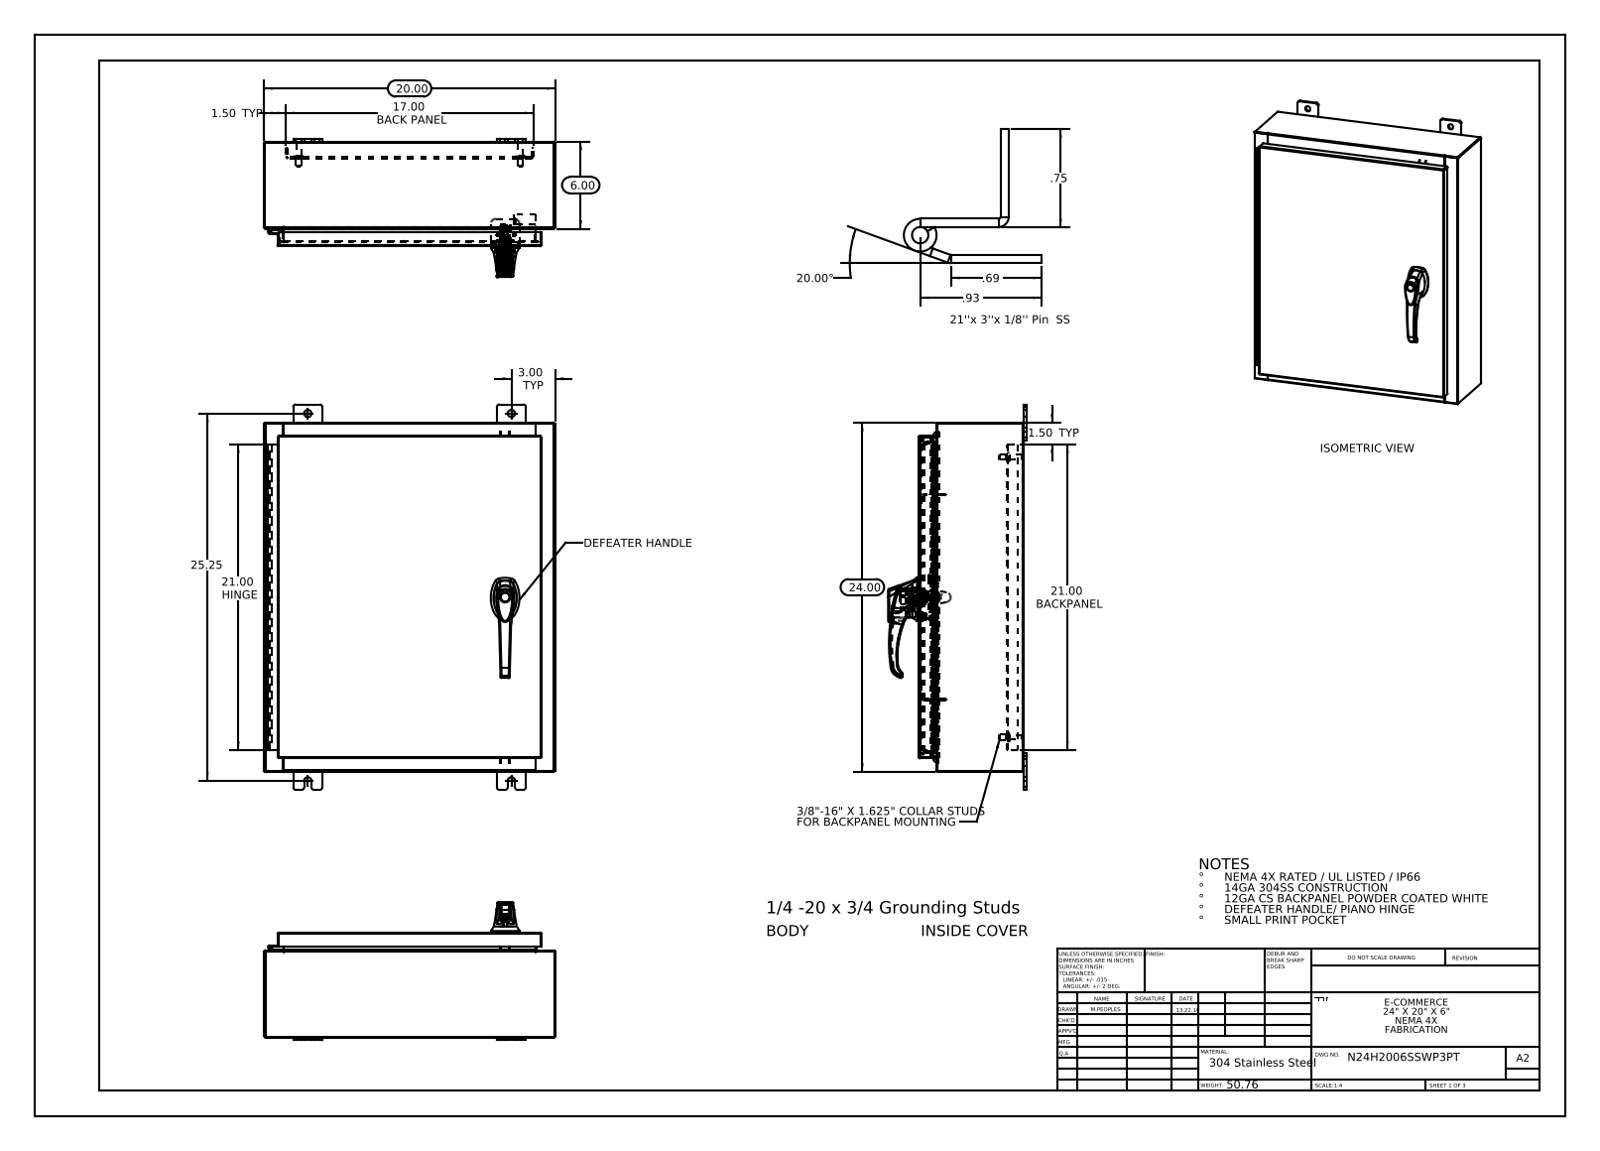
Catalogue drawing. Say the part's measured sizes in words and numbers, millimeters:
The part is named "NMP-SS-RODGUIDES; 297026; 012103_012102; N24H2006SSWP3PT Top (+8 more)". Its 3-D file was written by "SolidWorks 2013 (CONFIG_CONTROL_DESIGN)". It is 31 solids with 2412 faces: 865 planar, 893 cylindrical and 654 other. Overall it measures 673.1 by 508 by 241.2 millimeters. Its volume is 2 968 000 cubic millimeters and its surface area 2 872 000 square millimeters. Round holes: 8 of diameter 12.7, 4 of diameter 6.4, 3 of diameter 3.5, 3 of diameter 4.1, 2 of diameter 2, 2 of diameter 5.2, 2 of diameter 8, 2 of diameter 11.1, 1 of diameter 3.2, 1 of diameter 3.2, 1 of diameter 5, 1 of diameter 7. Round bosses or shafts: 4 of diameter 15.9, 4 of diameter 9.5, 4 of diameter 8.4, 1 of diameter 30, 1 of diameter 19, 1 of diameter 17.3, 1 of diameter 16.8, 1 of diameter 16.2. Partial cylindrical surfaces (rounded edges, fillets, slot ends): 37 of radius 3, 33 of radius 0.2, 24 of radius 4.8, 22 of radius 0.3, 18 of radius 2.2, 15 of radius 1, 12 of radius 0.7, 6 of radius 0.2. The main face-to-face distances are 1.9, 181, 179.1, 182.9, 2.6, 25.4, 27.3, 153.7, 155.6, 29.9. The hole center spacings are 195.1, 7.5, 15.9, 21.4, 31.8, 33.4, 39.6, 47.2.
